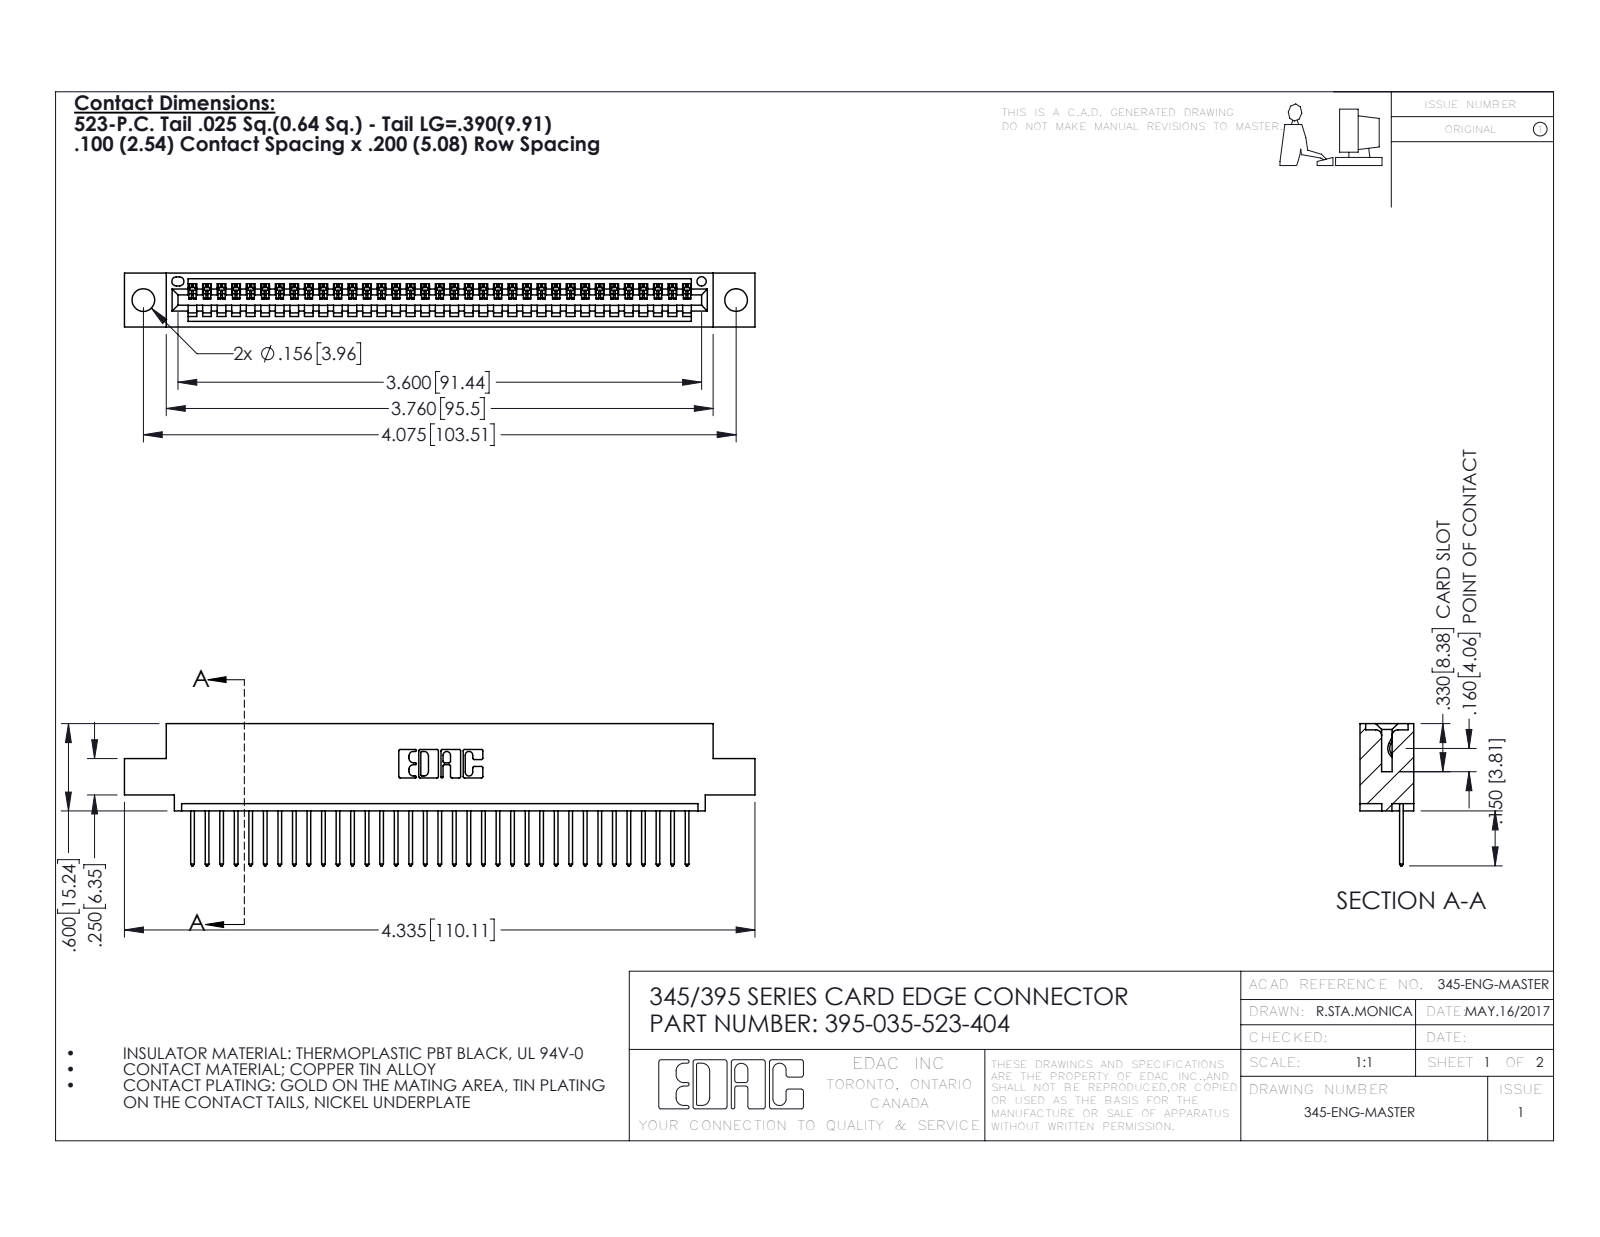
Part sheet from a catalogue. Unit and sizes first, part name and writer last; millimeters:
Units: millimetres
Overall size (bounding box): 110.1 × 24.8 × 9.4
Round holes (diameter × count): ⌀4 ×2, ⌀1.6 ×1
Partial cylindrical surfaces — rounded edges, fillets, slot ends (radius × count): R0.2 ×70, R0.3 ×70, R0.3 ×22, R0.2 ×6, R0.8 ×6, R0.7 ×3, R0.8 ×2, R1 ×2
Main face-to-face distances: 7.6, 1.8, 9.4, 2.5, 6.9, 0.6, 5.1, 5.7, 3.8, 1.8
Hole centre spacings: 6.9, 97.5, 103.5
Volume: 10 200 mm³ · Surface area: 13 430 mm²
Bodies: 36 solids, 2160 faces (1484 planar, 676 cylindrical, 0 other)
Part name (STEP PRODUCT): 345-292-001_345-293-123; 345 Part_0.110 Offset - 0.156 Dia-TH; 395-035-523-404
STEP written by: SolidWorks 2016 (CONFIG_CONTROL_DESIGN)
